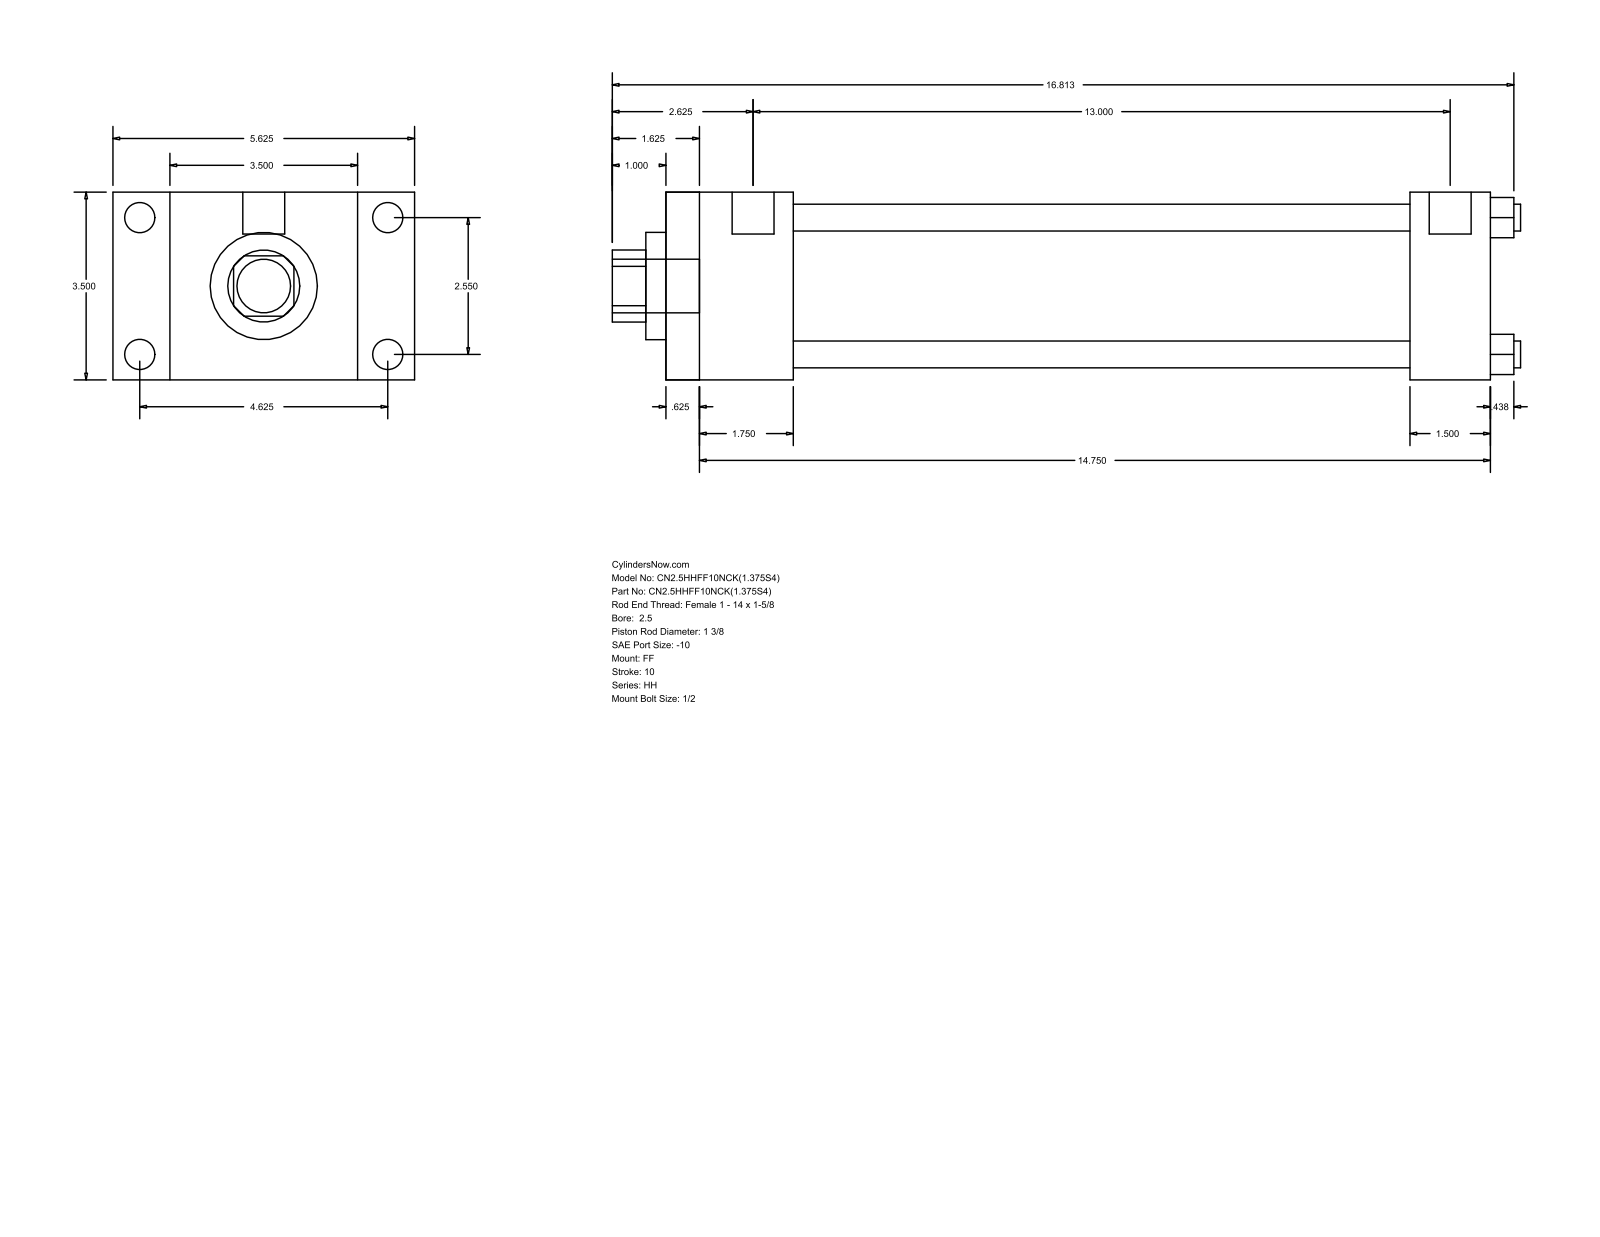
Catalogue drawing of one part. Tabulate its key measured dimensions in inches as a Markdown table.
| quantity | value |
| --- | --- |
| part name | HH_FF__0250_1.375 |
| STEP written by | GSSL Pune (CONFIG_CONTROL_DESIGN) |
| units | inches |
| bodies | 0 solids, 92 faces (64 planar, 28 cylindrical, 0 other) |
| overall size | 16.937 × 5.625 × 3.5 |
| round holes (diameter × count) | 0.5 × 4, 1.375 × 1, 2 × 1, 2.875 × 1 |
| round bosses / shafts (diameter × count) | 0.563 × 4, 0.219 × 4, 0.781 × 2, 1 × 1 |
| partial cylindrical surfaces (radius × count) | 0.672 × 1 |
| main face-to-face distances | 3.5, 15.375, 0.625, 14.75, 2.375, 1.75, 13, 13.875, 13.25, 11.5 |
| hole center spacings | 1.803, 2.55, 3.606 |
